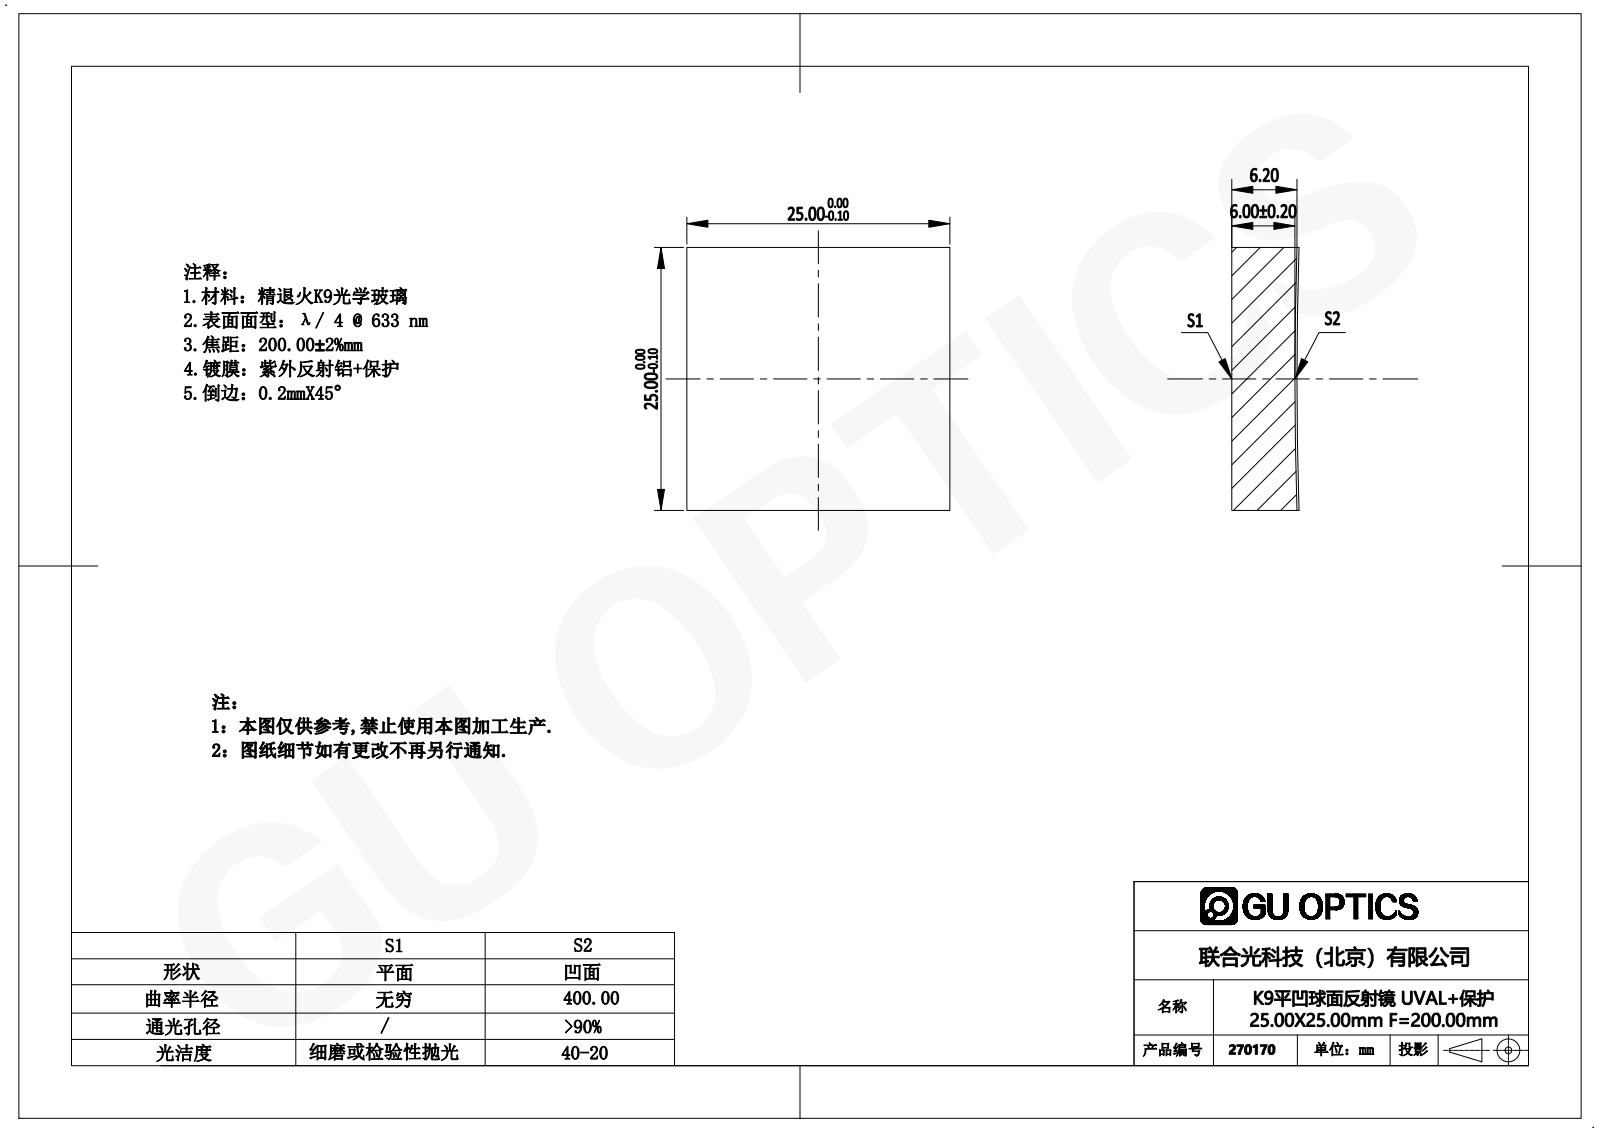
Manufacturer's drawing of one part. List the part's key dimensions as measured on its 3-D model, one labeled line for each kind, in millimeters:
Part name (STEP PRODUCT): 270040
STEP written by: SolidWorks 2019 (AUTOMOTIVE_DESIGN)
Units: millimetres
Bodies: 1 solid, 7 faces (5 planar, 0 cylindrical, 2 other)
Overall size (bounding box): 25 × 25 × 6.39
Volume: 3 831 mm³ · Surface area: 1 876 mm²
Main face-to-face distances: 25
